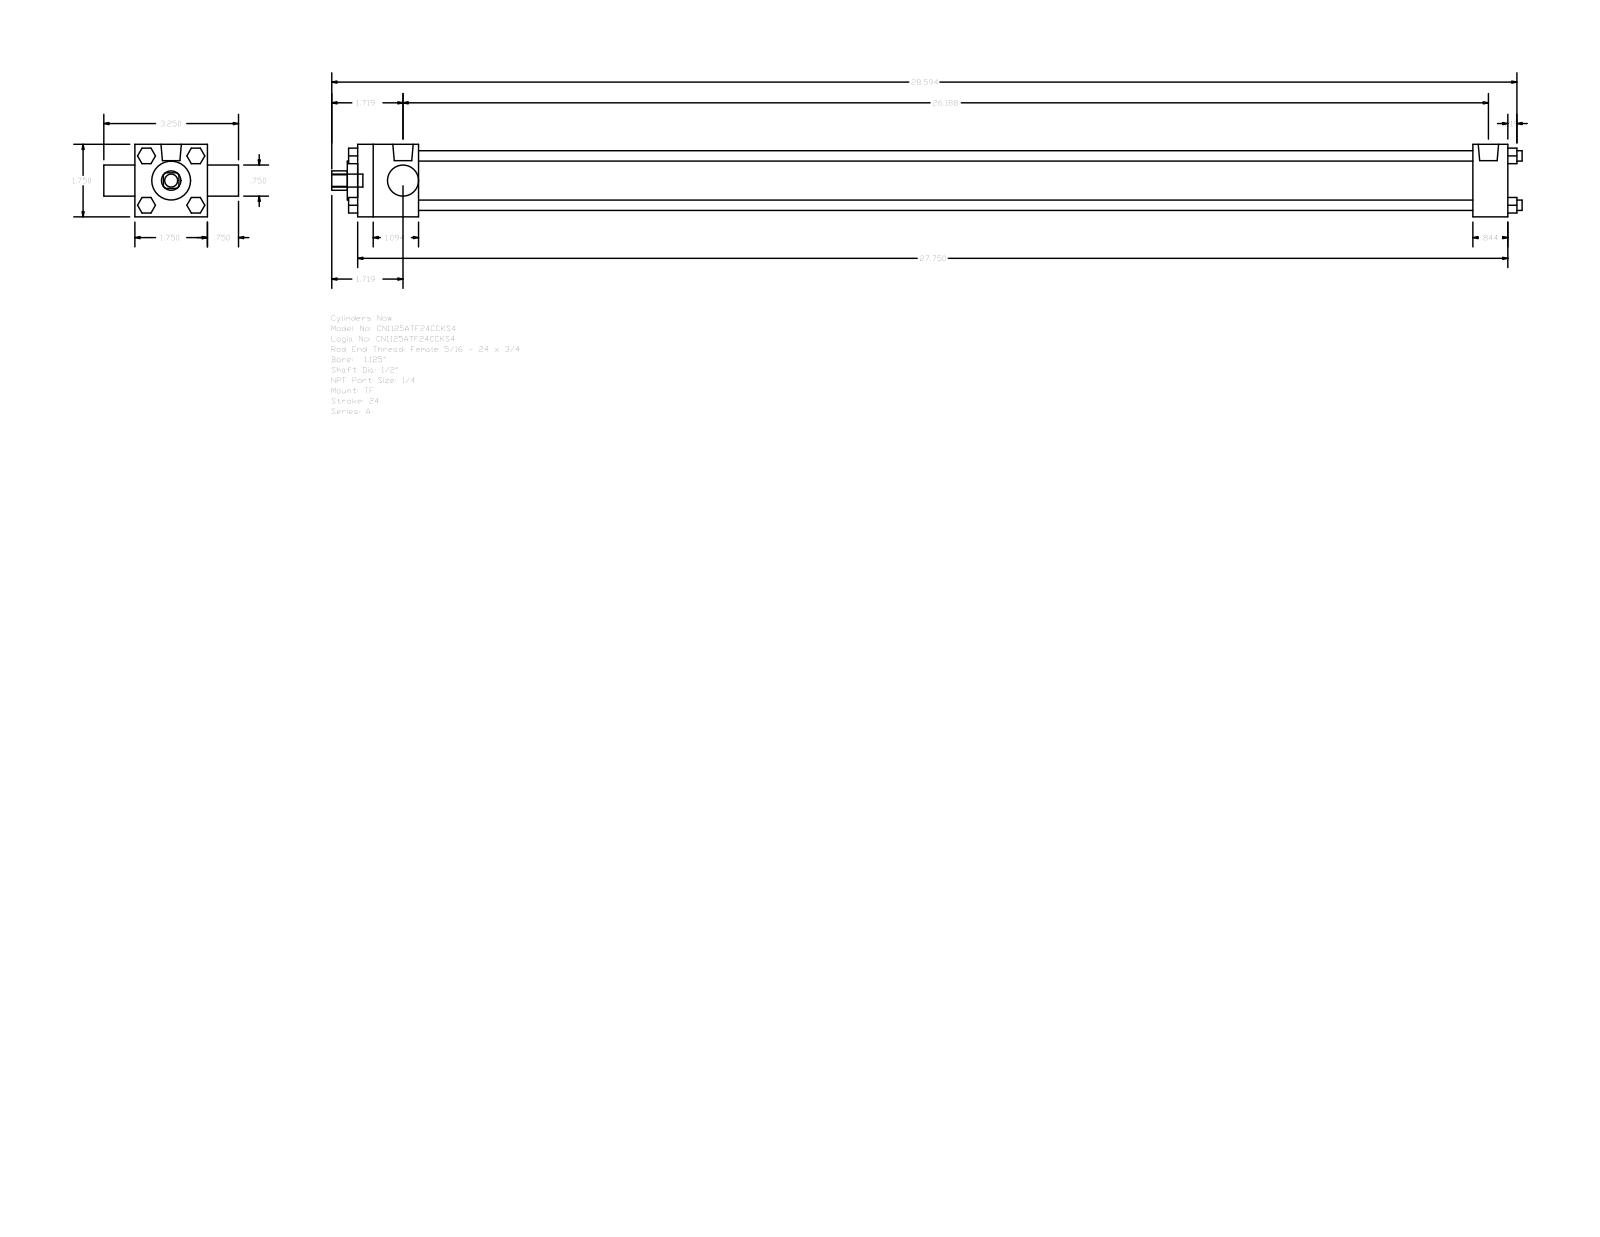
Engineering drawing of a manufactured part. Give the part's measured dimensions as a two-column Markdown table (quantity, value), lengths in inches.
| quantity | value |
| --- | --- |
| part name | A_TF__0112_0.5 |
| STEP written by | GSSL Pune (CONFIG_CONTROL_DESIGN) |
| units | inches |
| bodies | 0 solids, 120 faces (92 planar, 28 cylindrical, 0 other) |
| overall size | 28.719 × 3.25 × 1.75 |
| round holes (diameter × count) | 0.5 × 1, 0.75 × 1, 0.937 × 1, 1.255 × 1 |
| round bosses / shafts (diameter × count) | 0.25 × 4, 0.219 × 3, 0.492 × 2, 0.313 × 1 |
| partial cylindrical surfaces (radius × count) | 0.234 × 1 |
| main face-to-face distances | 1.75, 27.75, 26.906, 0.844, 1.469, 25.437, 26.281, 0.75, 2.5, 0.375 |
